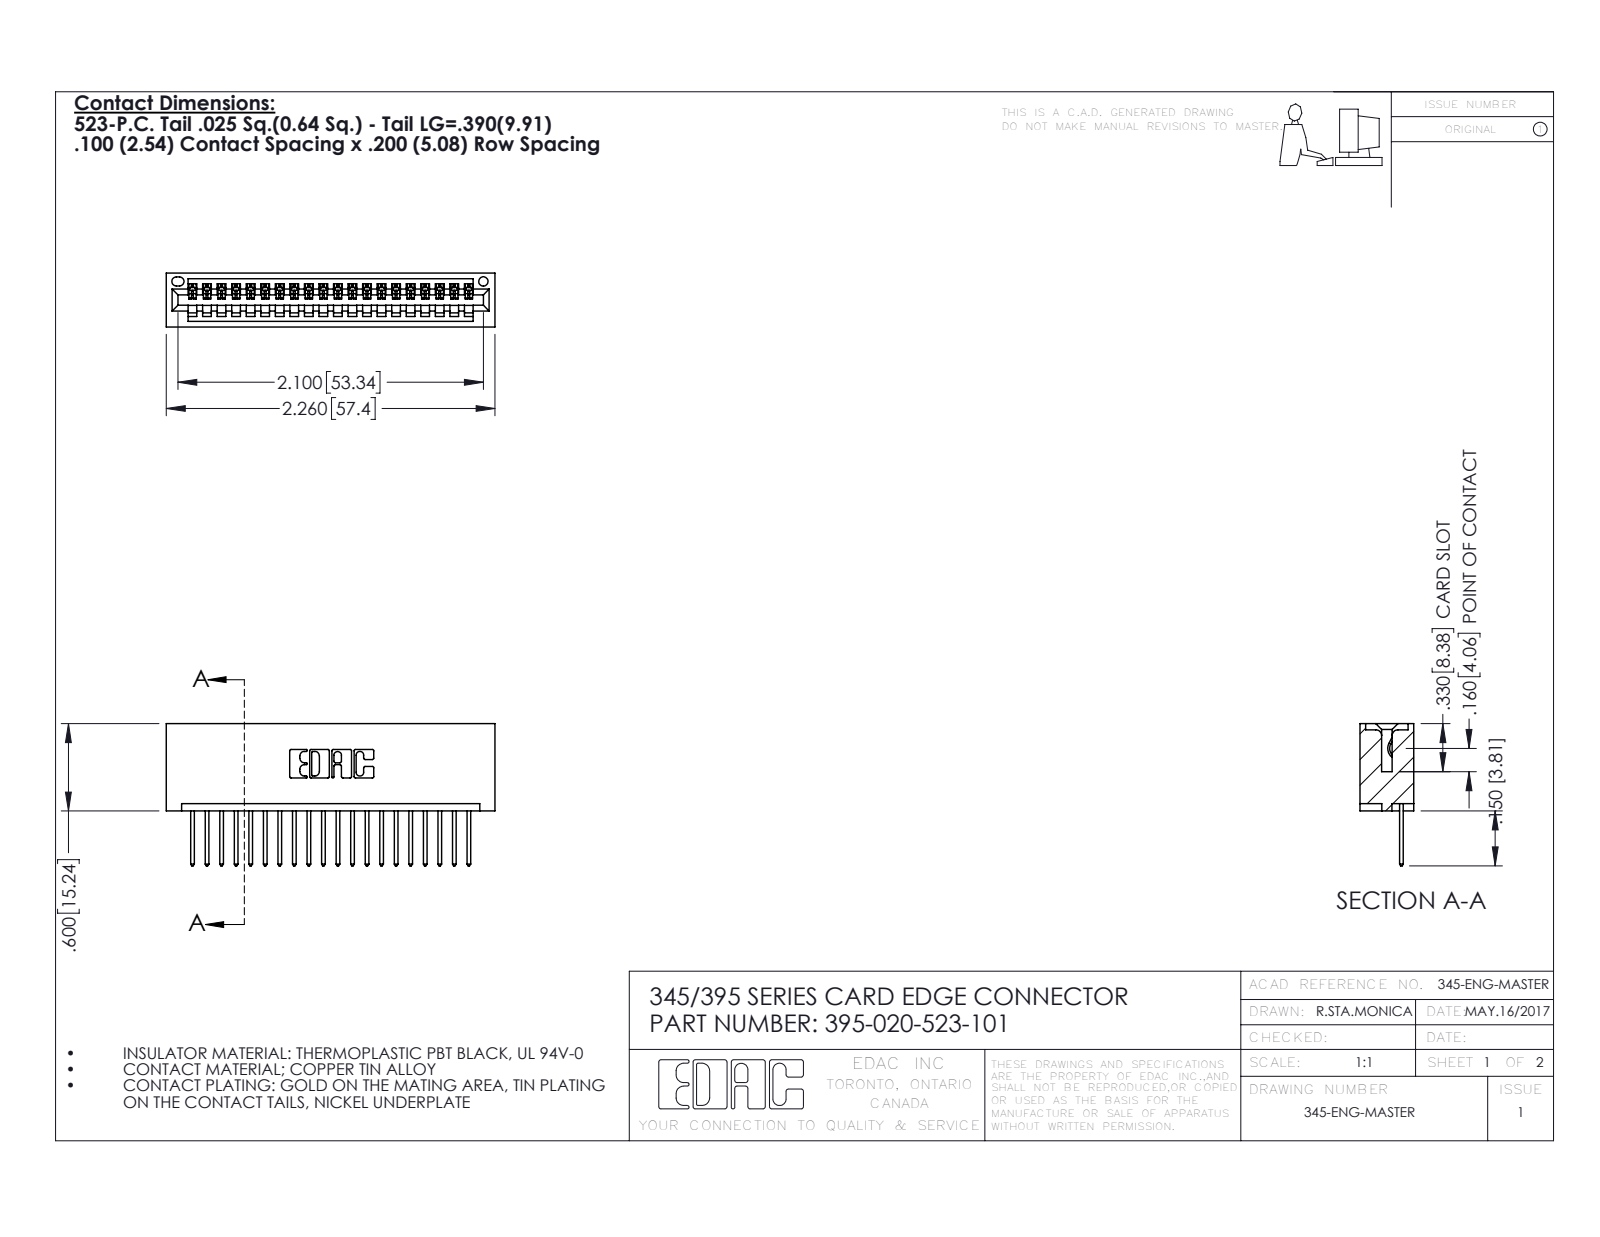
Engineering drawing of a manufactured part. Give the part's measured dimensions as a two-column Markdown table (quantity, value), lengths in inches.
| quantity | value |
| --- | --- |
| part name | 395-020-523-101; 345-292-001_345-293-123; 345 Part_No Mounting Lugs |
| STEP written by | SolidWorks 2016 (CONFIG_CONTROL_DESIGN) |
| units | inches |
| bodies | 21 solids, 1278 faces (876 planar, 402 cylindrical, 0 other) |
| overall size | 2.26 × 0.977 × 0.37 |
| volume | 0.357 in³ |
| surface area | 11.91 in² |
| round holes (diameter × count) | 0.064 × 1 |
| partial cylindrical surfaces (radius × count) | 0.006 × 40, 0.01 × 40, 0.01 × 22, 0.007 × 6, 0.031 × 6, 0.026 × 3, 0.031 × 2, 0.04 × 2 |
| main face-to-face distances | 0.298, 0.072, 0.2, 0.37, 0.098, 0.272, 0.025, 0.225, 0.1, 0.149 |
